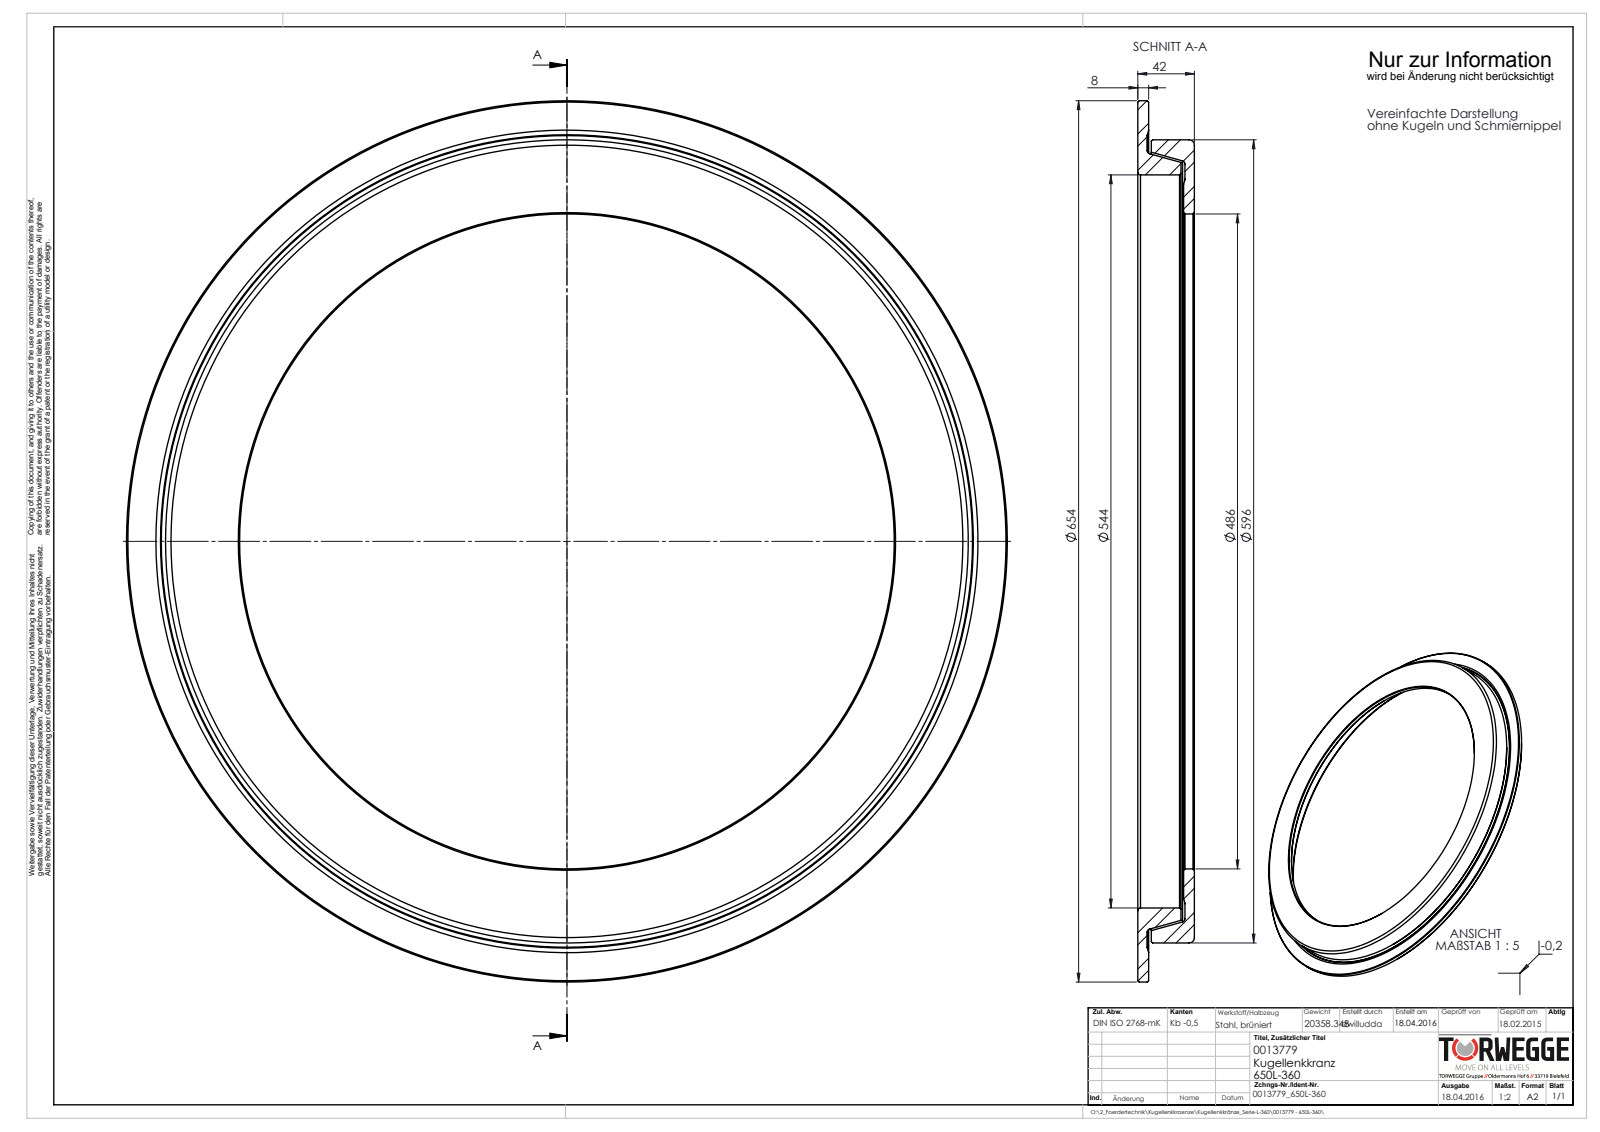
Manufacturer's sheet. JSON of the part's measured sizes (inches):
{"part_name": "0013779_650L-360", "step_written_by": "SolidWorks 2016 (AUTOMOTIVE_DESIGN)", "units": "inches", "bodies": {"solids": 2, "faces": 48, "planar": 8, "cylindrical": 8, "other": 32}, "overall_size": [25.748, 25.748, 1.654], "volume_in3": 157.9, "surface_area_in2": 919, "round_holes": [[19.134, 1], [21.417, 1]], "round_bosses_or_shafts": [[25.748, 1], [23.465, 1]], "face_to_face_distances": [1.654, 0.315, 1.339, 0.276, 1.378, 0.039, 1.063, 1.024, 0.394, 1.26]}
